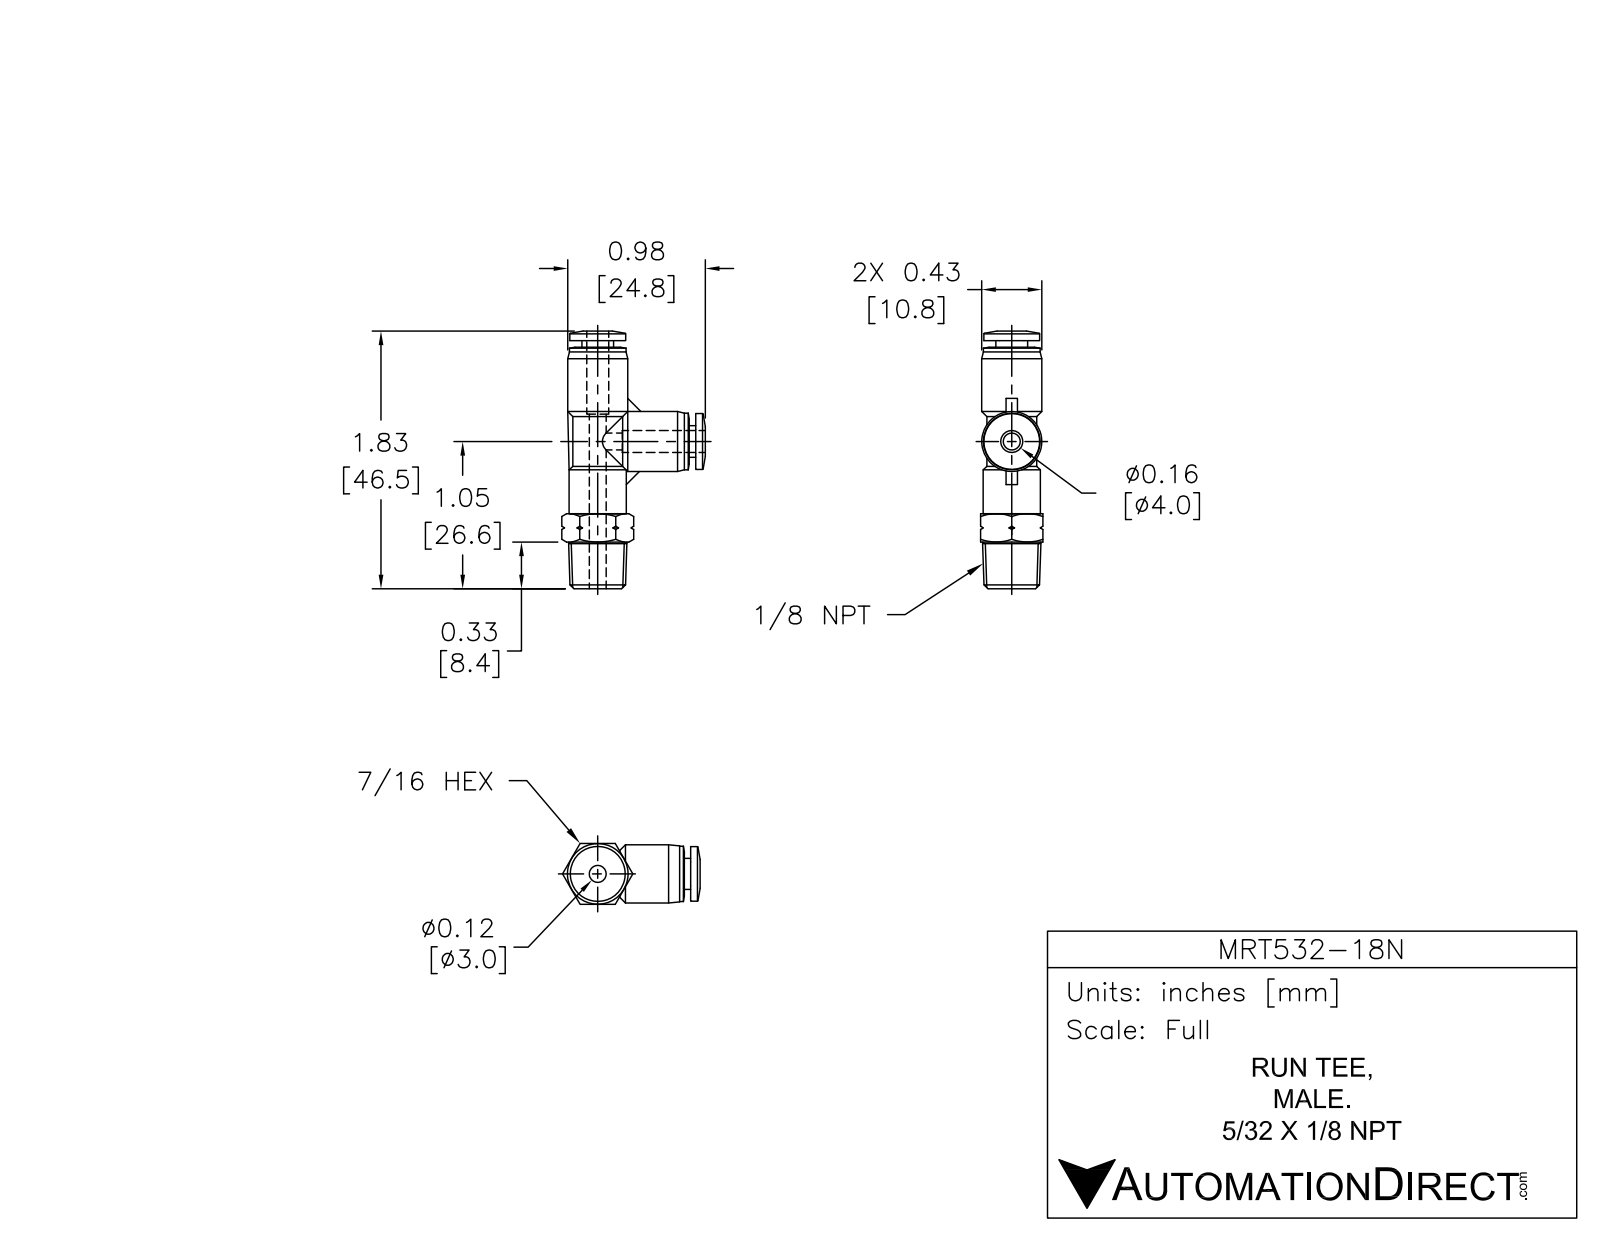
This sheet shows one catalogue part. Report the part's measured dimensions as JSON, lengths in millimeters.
{"part_name": "MRT532-18N", "step_written_by": "SolidWorks 2015 (AUTOMOTIVE_DESIGN)", "units": "millimeters", "bodies": {"solids": 1, "faces": 116, "planar": 23, "cylindrical": 30, "other": 63}, "overall_size": [45.5, 25.9, 11], "volume_mm3": 4150, "surface_area_mm2": 3038, "round_holes": [[3, 2], [4.3, 2]], "round_bosses_or_shafts": [[10.6, 2], [10, 2], [9.9, 2], [8.8, 2], [5.6, 2], [10.1, 1]], "face_to_face_distances": [11, 1.1, 43.8, 4.5, 6.5, 42.6, 13.5, 29.2, 30.3, 11.9]}
